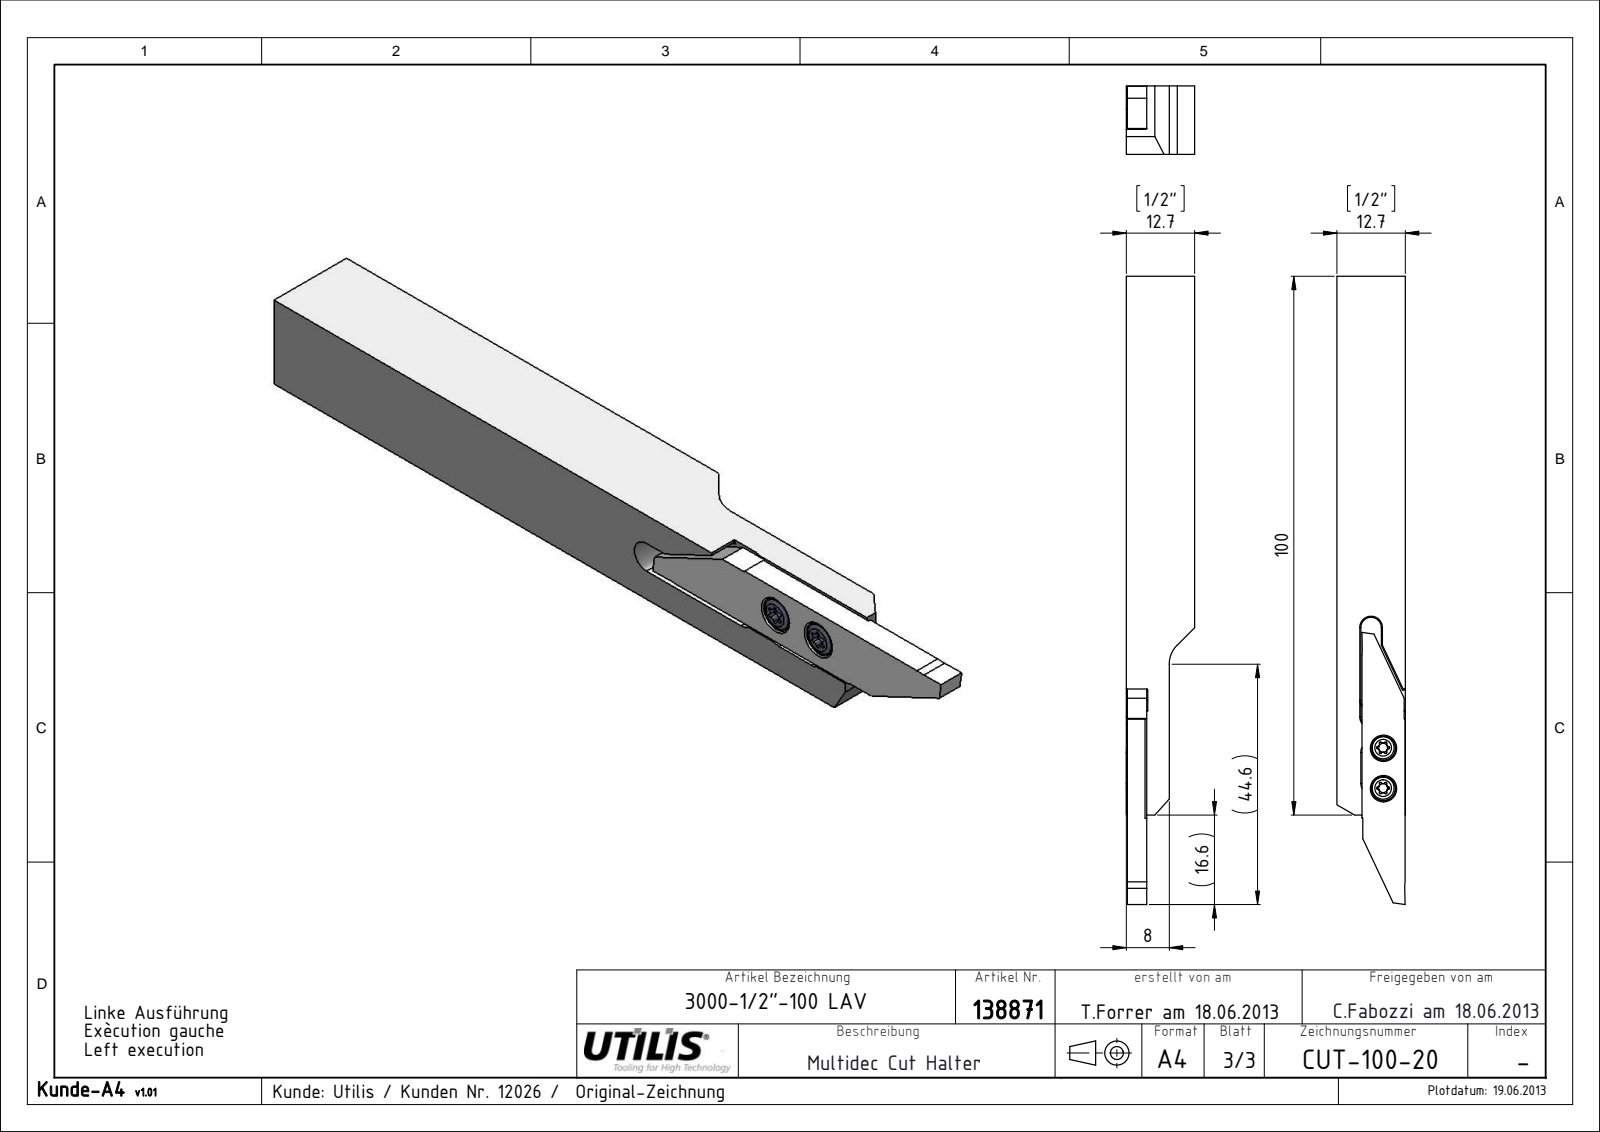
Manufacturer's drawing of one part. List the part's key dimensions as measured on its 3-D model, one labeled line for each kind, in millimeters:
Part name (STEP PRODUCT): CUT-100-Kunde_3000-1-2-100 LAV; CUT- 3000 R+L Lang NUR FÜR KUNDEN _L-Lang; MSP-16_M3x7.3 T08; CUT-100-20
STEP written by: SolidWorks 2014 (CONFIG_CONTROL_DESIGN)
Units: millimetres
Bodies: 4 solids, 118 faces (34 planar, 56 cylindrical, 28 other)
Overall size (bounding box): 116.6 × 12.7 × 12.7
Volume: 14 247 mm³ · Surface area: 6 428 mm²
Round holes (diameter × count): ⌀2.5 ×2, ⌀4.9 ×2
Round bosses / shafts (diameter × count): ⌀4.1 ×2, ⌀3 ×2
Partial cylindrical surfaces — rounded edges, fillets, slot ends (radius × count): R0.2 ×12, R0.45 ×12, R2.1 ×4, R10 ×2, R5 ×1
Main face-to-face distances: 12.7, 3.8, 8.9, 8, 4.2, 4.7, 3.6, 7.8, 12.5, 4.65
Hole centre spacings: 3.75, 7.5, 3.65, 3.85, 7.4, 7.6
